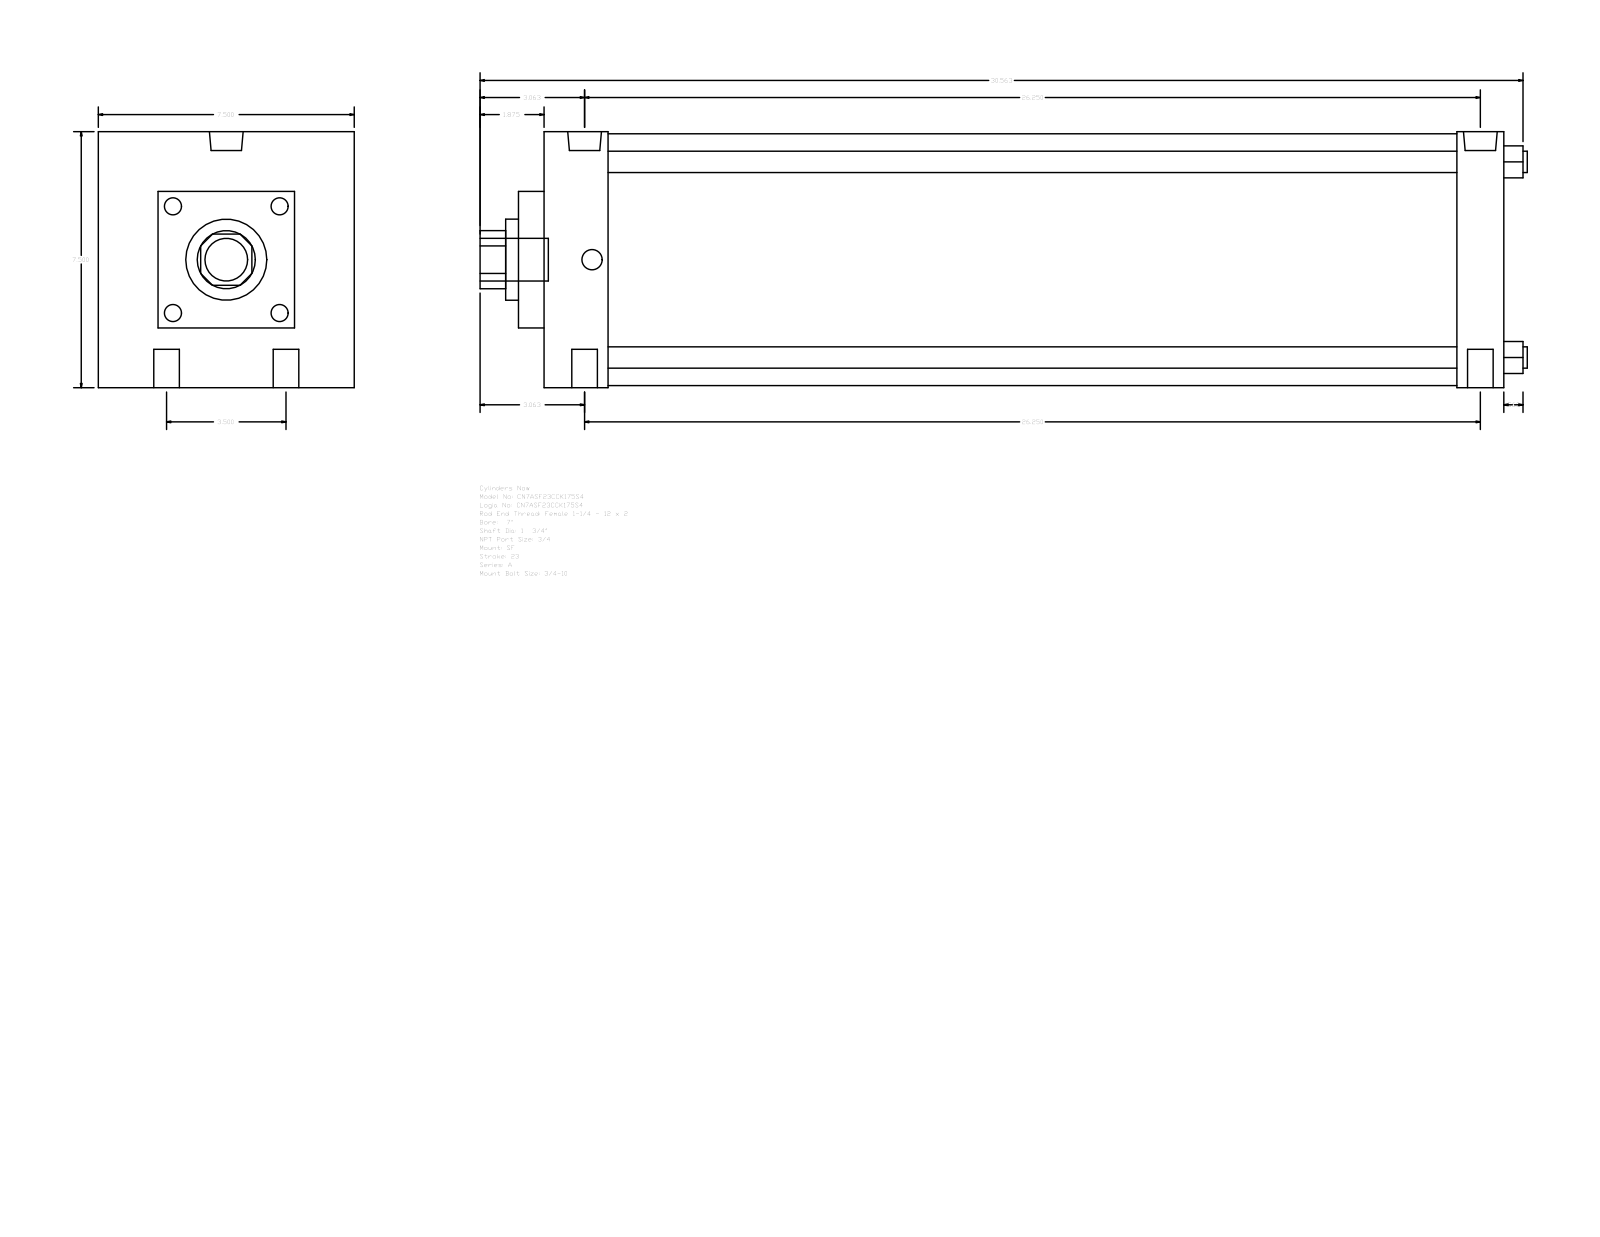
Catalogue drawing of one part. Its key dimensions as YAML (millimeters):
part_name: "A_SF__0700_1.75"
step_written_by: "GSSL Pune (CONFIG_CONTROL_DESIGN)"
units: millimeters
bodies: {solids: 0, faces: 93, planar: 67, cylindrical: 26, other: 0}
overall_size: [779.46, 190.5, 190.5]
round_holes:
  - {diameter: 19.05, count: 4}
  - {diameter: 15.08, count: 2}
  - {diameter: 25.12, count: 2}
  - {diameter: 44.45, count: 1}
  - {diameter: 60.33, count: 1}
round_bosses_or_shafts:
  - {diameter: 15.88, count: 4}
  - {diameter: 187.32, count: 1}
  - {diameter: 31.75, count: 1}
partial_cylinders:
  - {radius: 21.63, count: 1}
face_to_face_distances: [190.5, 714.38, 44.45, 34.92, 19.05, 47.63, 679.46, 631.83, 666.75, 146.05]
hole_center_spacings: [44.45, 668.23, 666.75, 88.9, 672.65, 655.63]
